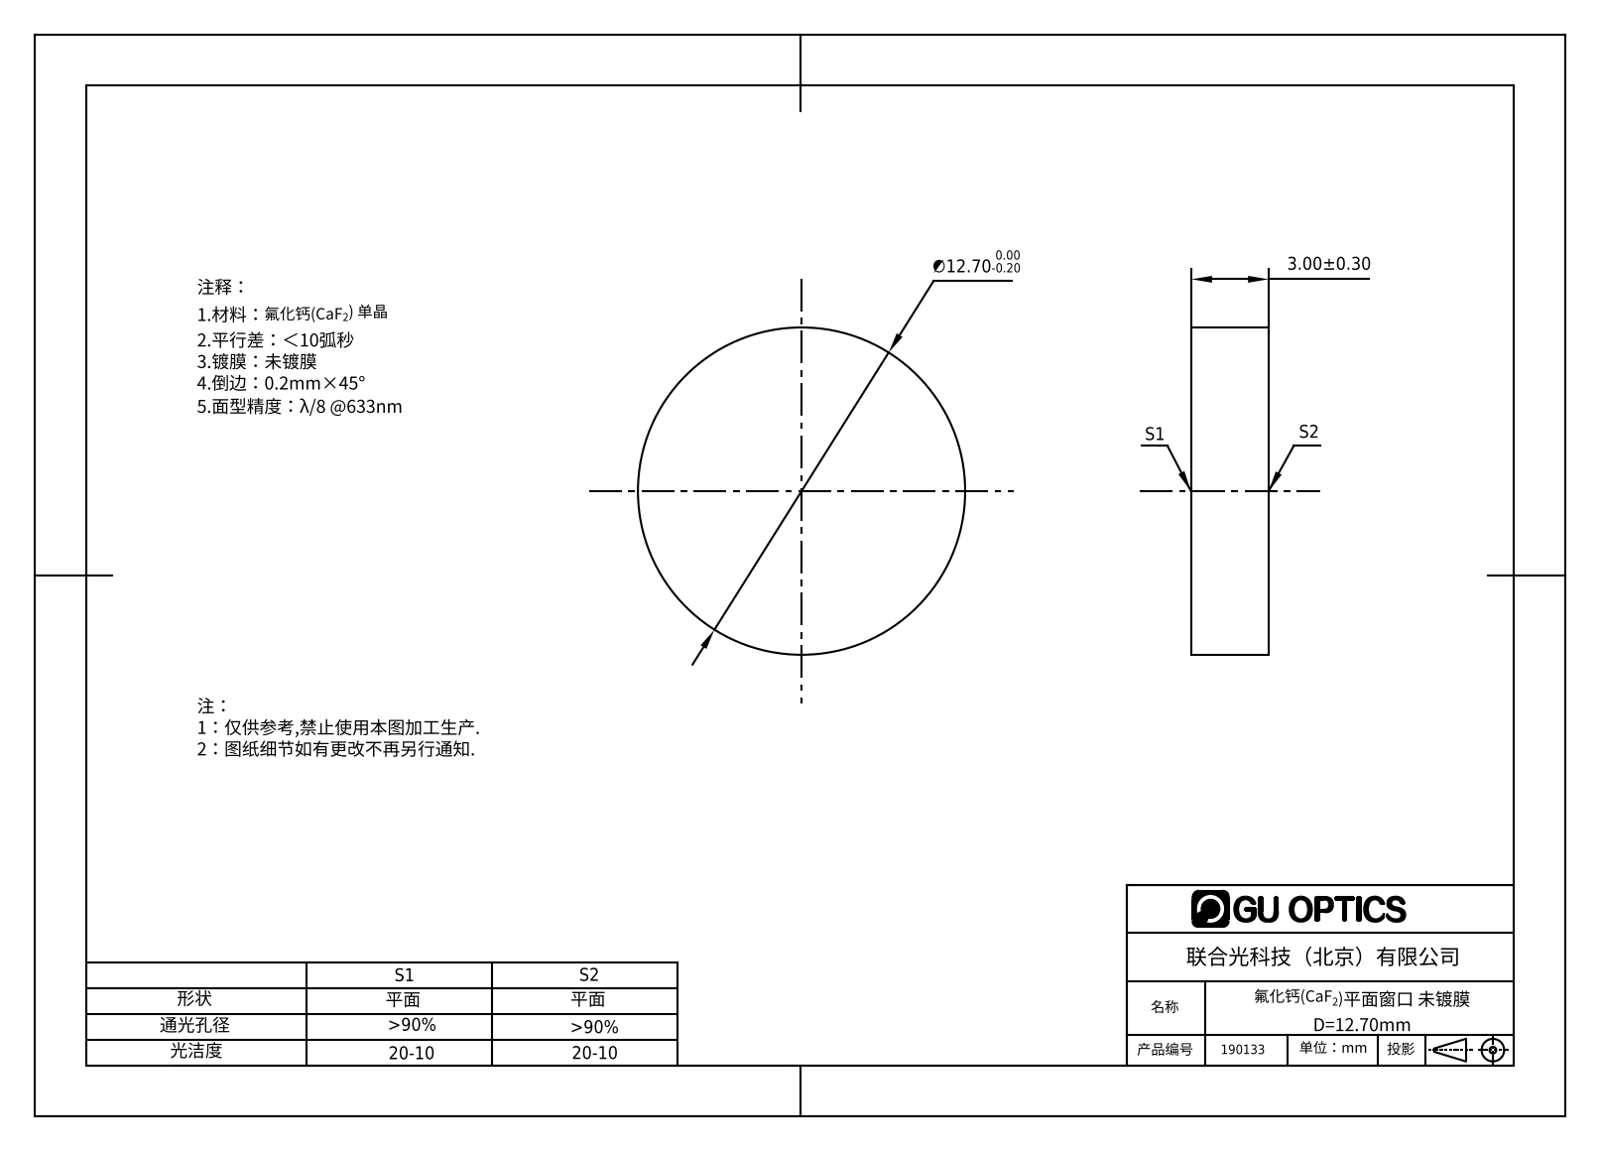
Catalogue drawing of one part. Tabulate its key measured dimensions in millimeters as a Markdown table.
| quantity | value |
| --- | --- |
| part name | 190133 |
| STEP written by | SolidWorks 2016 (AUTOMOTIVE_DESIGN) |
| units | millimeters |
| bodies | 1 solid, 4 faces (2 planar, 2 cylindrical, 0 other) |
| overall size | 12.7 × 12.7 × 3 |
| volume | 380 mm³ |
| surface area | 373 mm² |
| round bosses / shafts (diameter × count) | 12.7 × 1 |
| main face-to-face distances | 3 |
